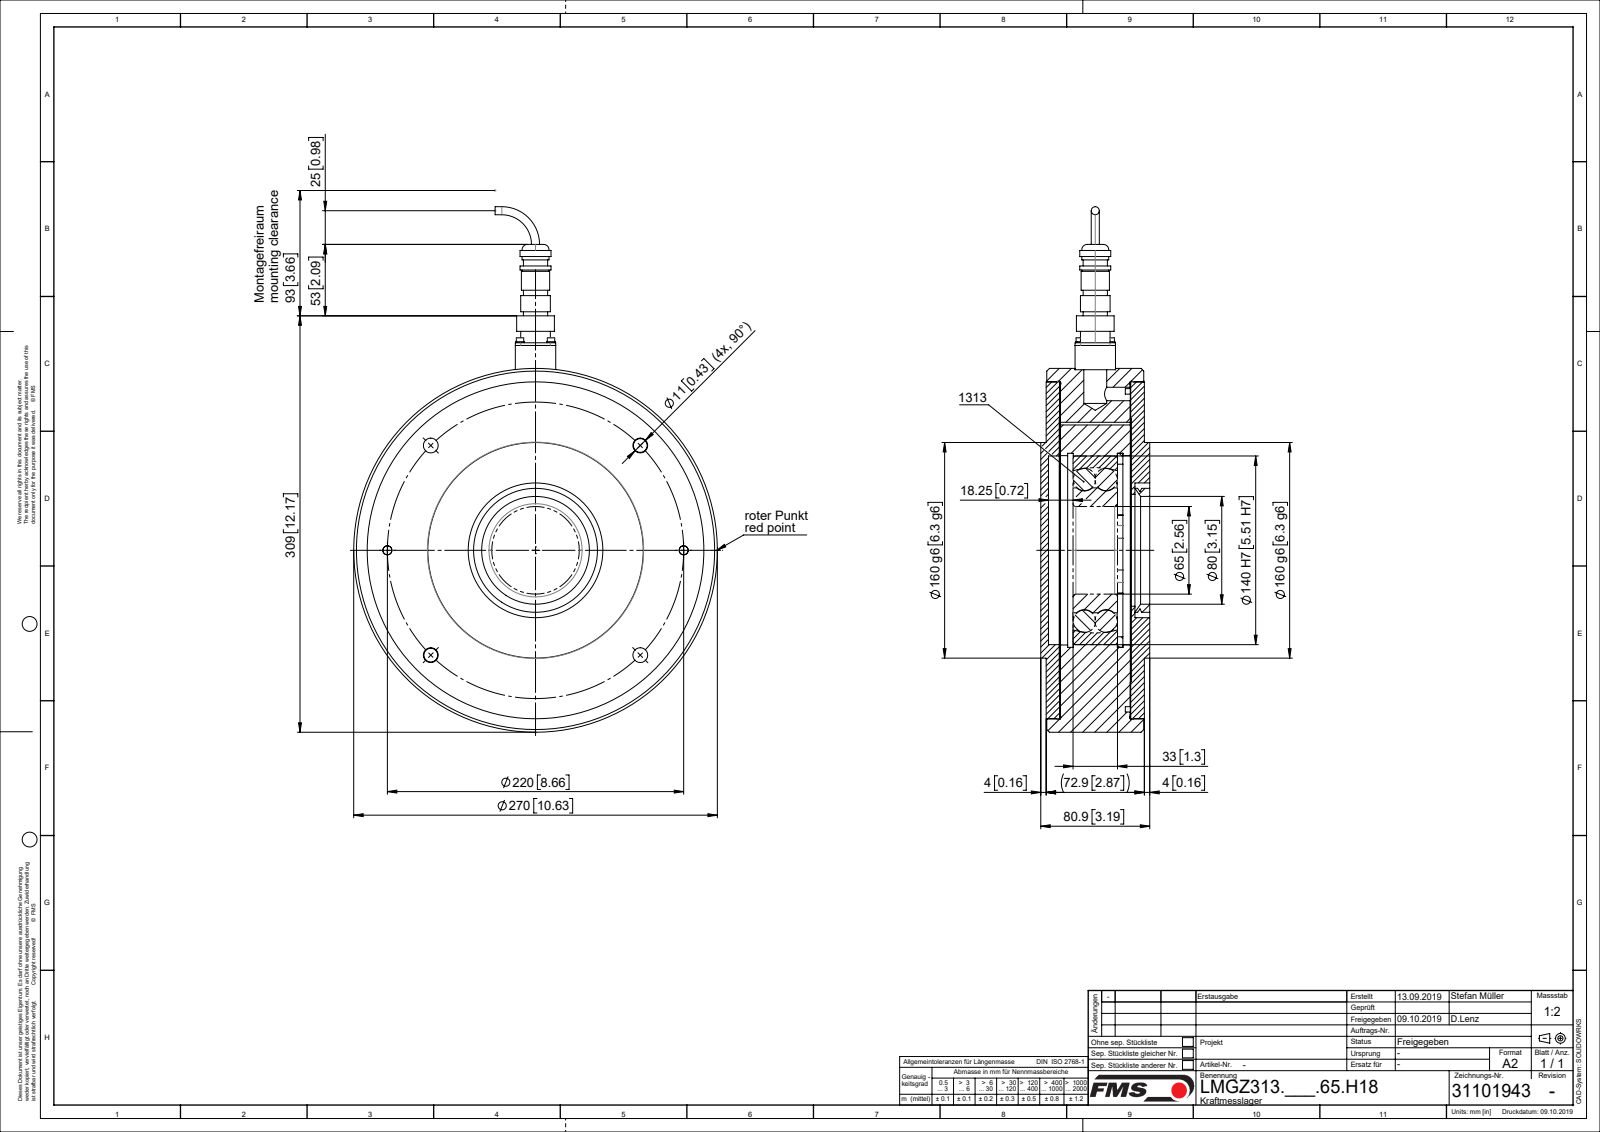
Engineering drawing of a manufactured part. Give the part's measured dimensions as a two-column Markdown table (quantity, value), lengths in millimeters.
| quantity | value |
| --- | --- |
| part name | ZEICHNUNG2; L50008; L4899004; TEIL1 (+8 more) |
| STEP written by | Mechanical Desktop 2009 (CONFIG_CONTROL_DESIGN) |
| units | millimeters |
| bodies | 20 solids, 369 faces (89 planar, 224 cylindrical, 56 other) |
| overall size | 390 × 270 × 80.8 |
| volume | 3 681 000 mm³ |
| surface area | 573 995 mm² |
| round holes (diameter × count) | 2.6 × 4, 3.2 × 4, 3.4 × 4, 11 × 4, 12 × 4, 6.91 × 2, 9 × 2, 10 × 2, 15 × 2, 65 × 1, 80 × 1, 83 × 1 |
| round bosses / shafts (diameter × count) | 6.2 × 4, 5.5 × 4, 3 × 4, 2.5 × 4, 13 × 2, 8 × 2, 270 × 1, 250 × 1 |
| partial cylindrical surfaces (radius × count) | 4 × 4 |
| main face-to-face distances | 52.3, 10.3, 52.8, 52, 0.5, 9.5, 4, 62.8, 10, 62.3 |
| hole center spacings | 110, 23, 84.19, 155.56, 203.25, 220, 32.53 |
